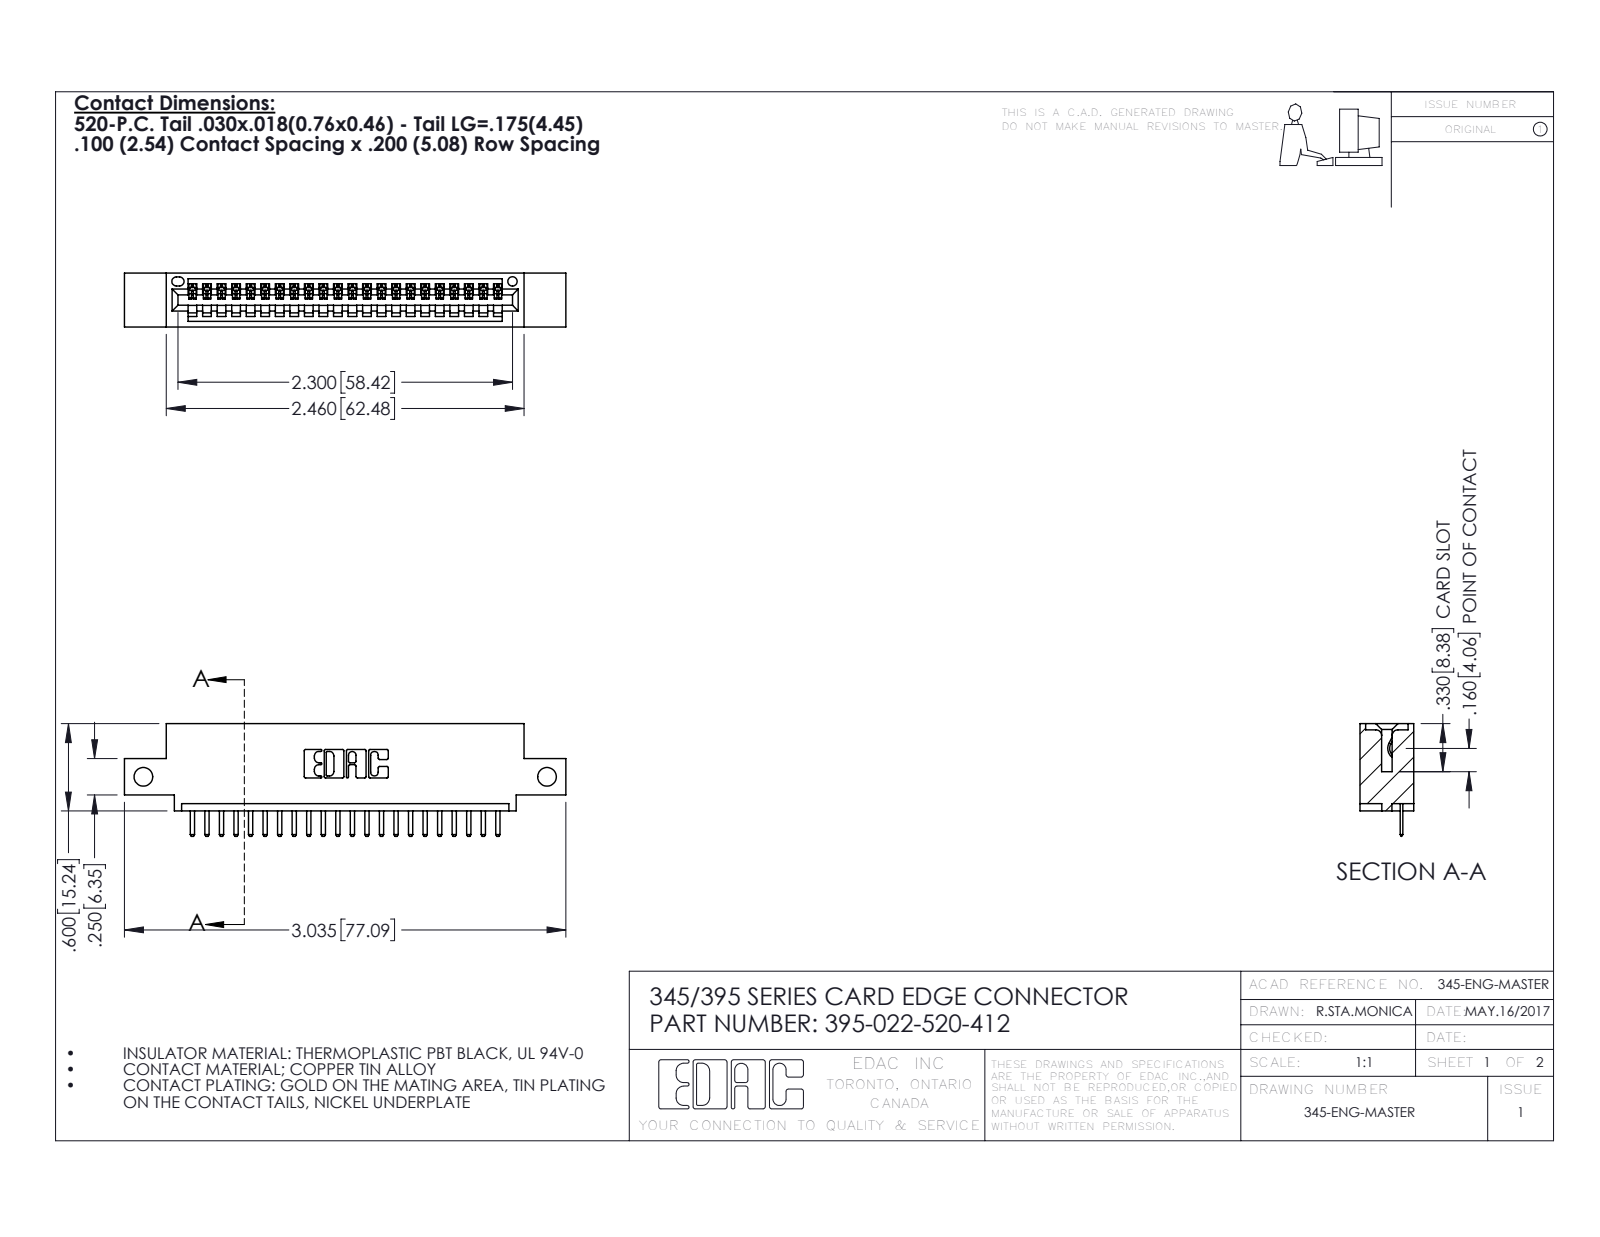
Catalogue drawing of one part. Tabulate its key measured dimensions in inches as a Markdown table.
| quantity | value |
| --- | --- |
| part name | 345 Part_0.110 Offset - Side Mount; 395-022-520-412; 345-292-001_345-293-120 |
| STEP written by | SolidWorks 2016 (CONFIG_CONTROL_DESIGN) |
| units | inches |
| bodies | 23 solids, 1494 faces (1008 planar, 486 cylindrical, 0 other) |
| overall size | 3.035 × 0.775 × 0.37 |
| volume | 0.423 in³ |
| surface area | 13.45 in² |
| round holes (diameter × count) | 0.128 × 2, 0.064 × 1 |
| partial cylindrical surfaces (radius × count) | 0.01 × 46, 0.006 × 44, 0.01 × 22, 0.007 × 6, 0.031 × 6, 0.026 × 3, 0.031 × 2, 0.04 × 2 |
| main face-to-face distances | 0.072, 0.298, 0.37, 0.2, 0.098, 0.272, 0.025, 0.225, 0.072, 0.149 |
| hole center spacings | 2.775 |
